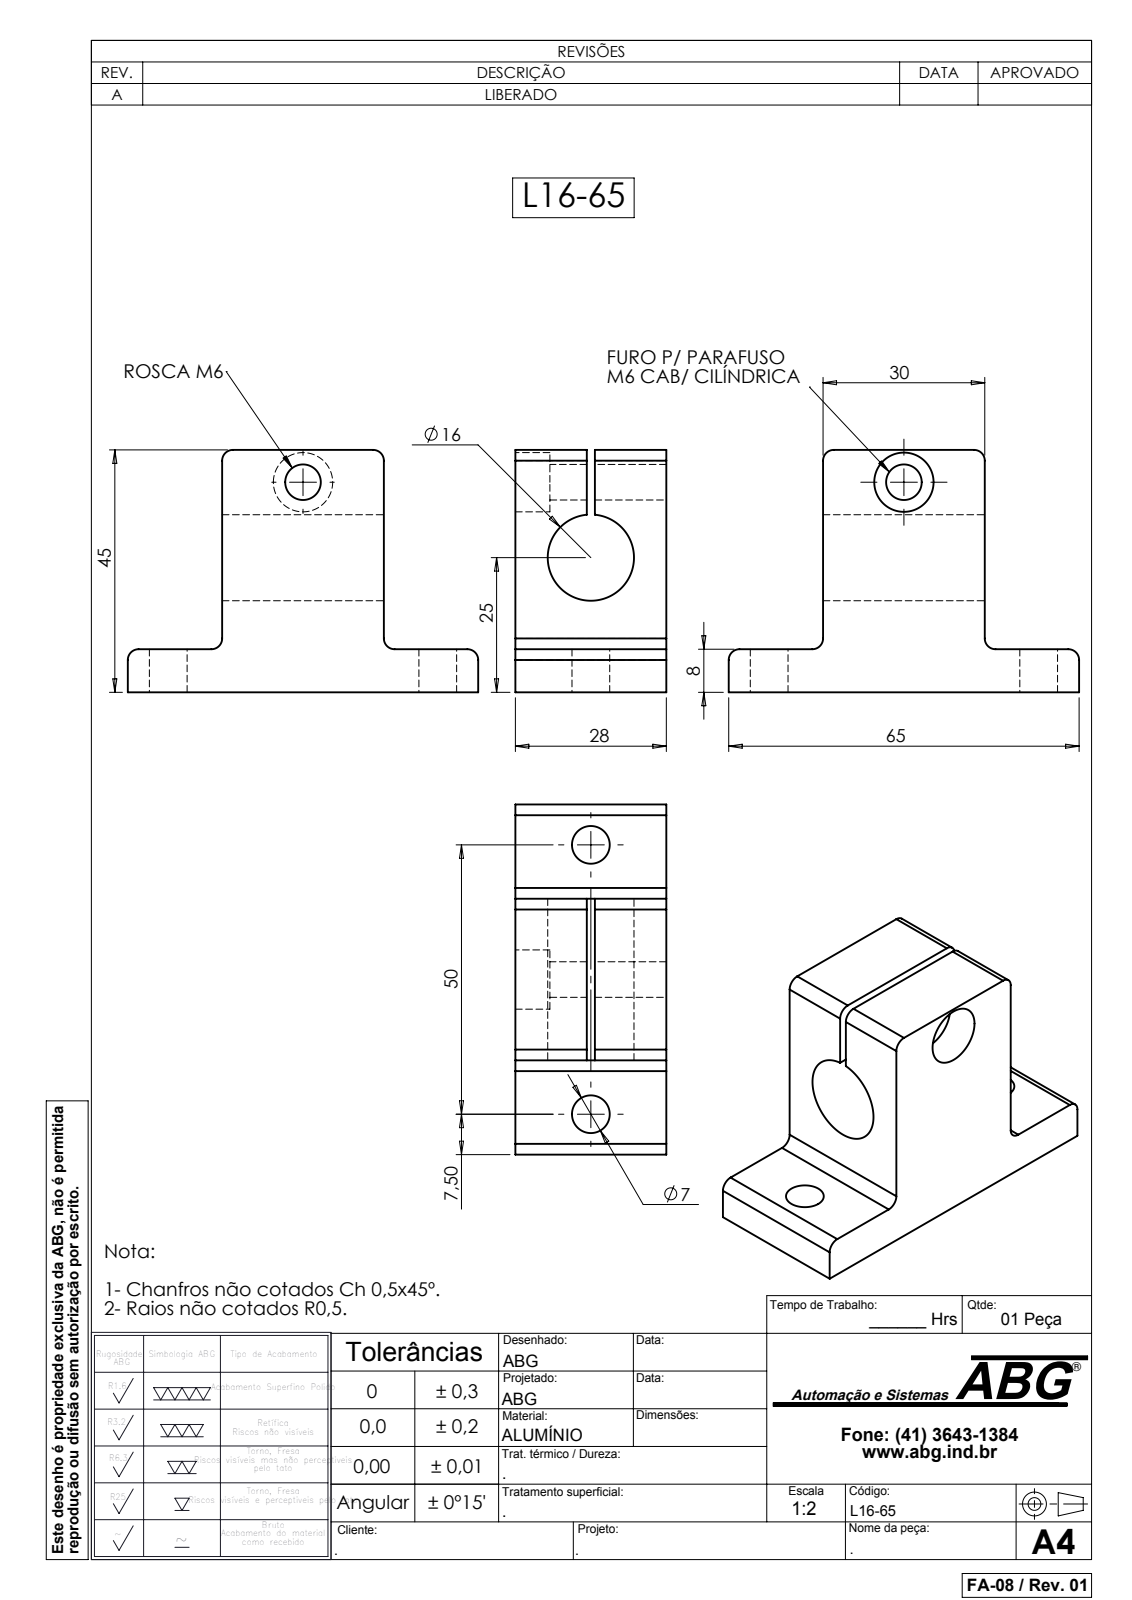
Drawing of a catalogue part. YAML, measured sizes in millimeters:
part_name: "L16-65"
step_written_by: "SolidWorks 2007 (CONFIG_CONTROL_DESIGN)"
units: millimeters
bodies: {solids: 1, faces: 33, planar: 14, cylindrical: 19, other: 0}
overall_size: [65, 45, 28]
volume: 37110
surface_area: 11672
round_holes:
  - {diameter: 7, count: 2}
  - {diameter: 6.6, count: 1}
  - {diameter: 11, count: 1}
  - {diameter: 16, count: 1}
partial_cylinders:
  - {radius: 2, count: 6}
face_to_face_distances: [28, 30, 45, 8, 37, 13.25, 14.75, 17.5, 47.5, 1.5]
hole_center_spacings: [50]
